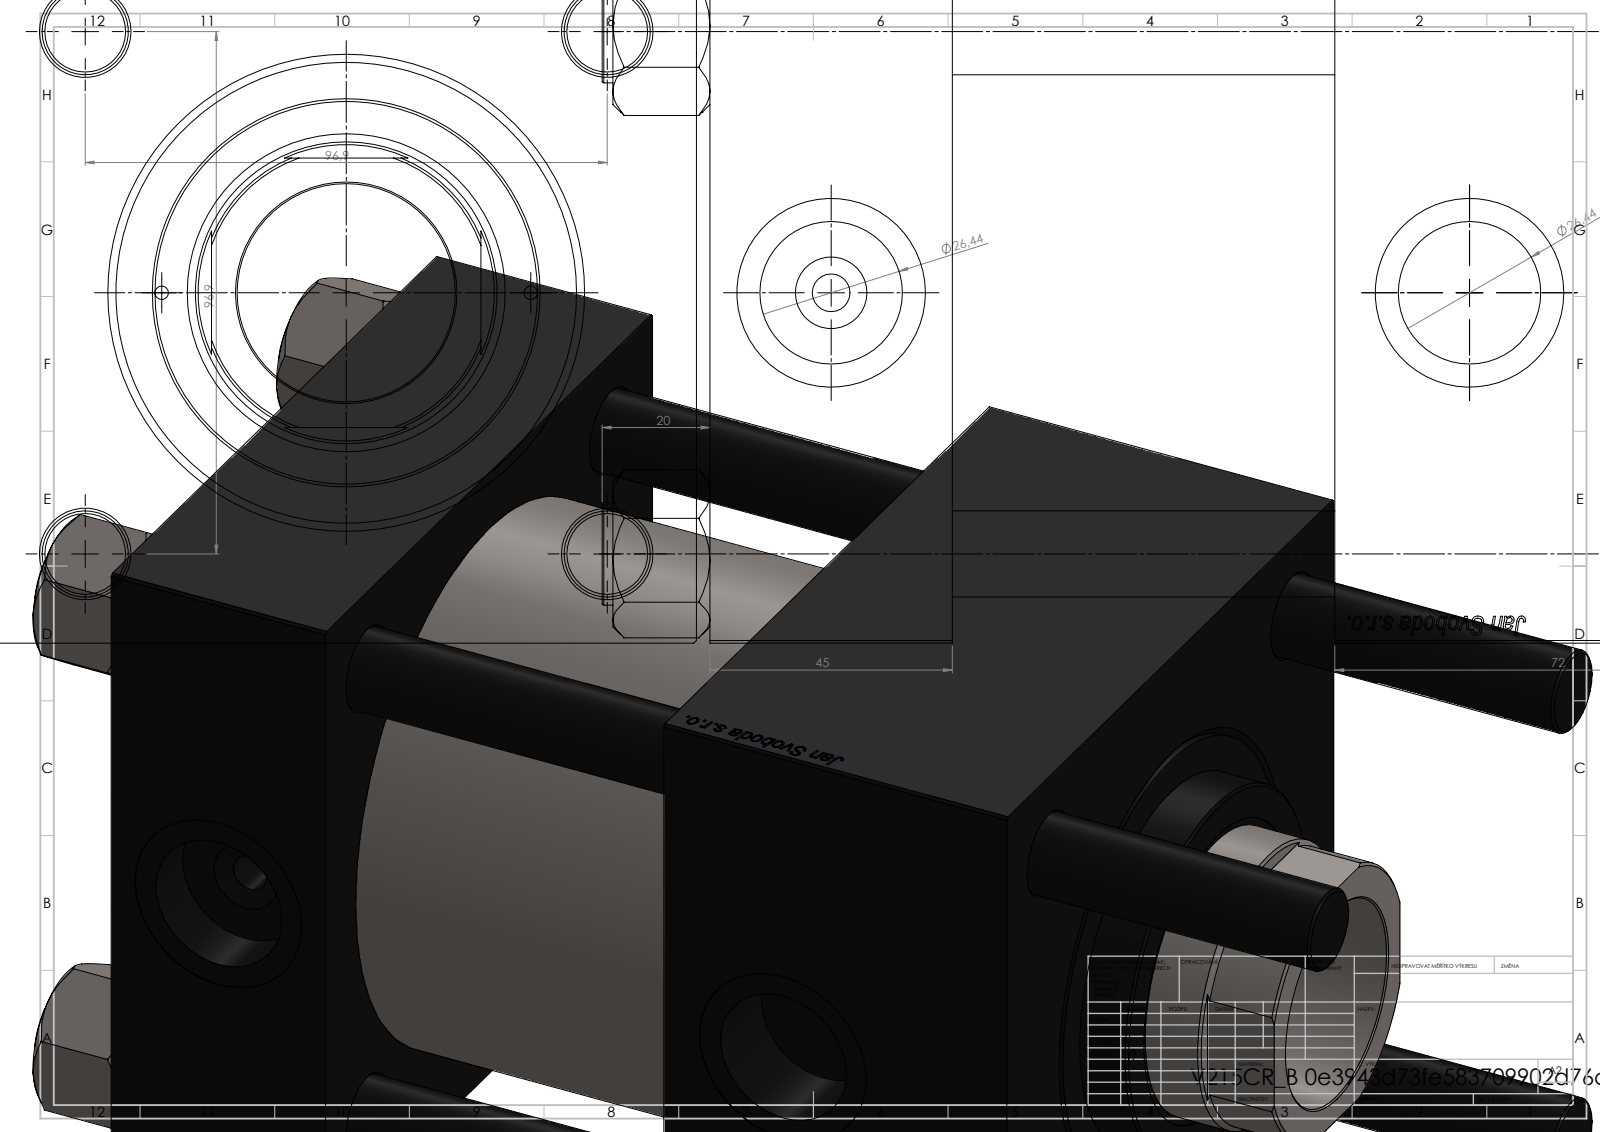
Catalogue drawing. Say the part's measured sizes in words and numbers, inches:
The part is named "V215_VC_A; V215CR_VCP_B; NUT_M5_B; V215CR_B-1 (+1 more)". Its 3-D file was written by "SolidWorks 2019 (CONFIG_CONTROL_DESIGN)". It is 11 solids with 1212 faces: 482 planar, 82 cylindrical and 648 other. Overall it measures 10.512 by 5.118 by 5.118 inches. Its volume is 155.9 cubic inches and its surface area 558.9 square inches. Round holes: 4 of diameter 0.63, 2 of diameter 0.098, 2 of diameter 0.276, 2 of diameter 1.041, 2 of diameter 1.378, 1 of diameter 1.594, 1 of diameter 2.205, 1 of diameter 2.323, 1 of diameter 2.992, 1 of diameter 3.366, 1 of diameter 3.937. Round bosses or shafts: 4 of diameter 0.748, 1 of diameter 4.173, 1 of diameter 2.835. Partial cylindrical surfaces (rounded edges, fillets, slot ends): 1 of radius 1.063. The main face-to-face distances are 5.118, 1.772, 7.402, 5.63, 4.567, 2.795, 2.835, 0.787, 2.008, 3.78. The hole center spacings are 1.988, 2.698, 3.774, 3.815, 1.348, 5.395, 2.697, 4.665.
